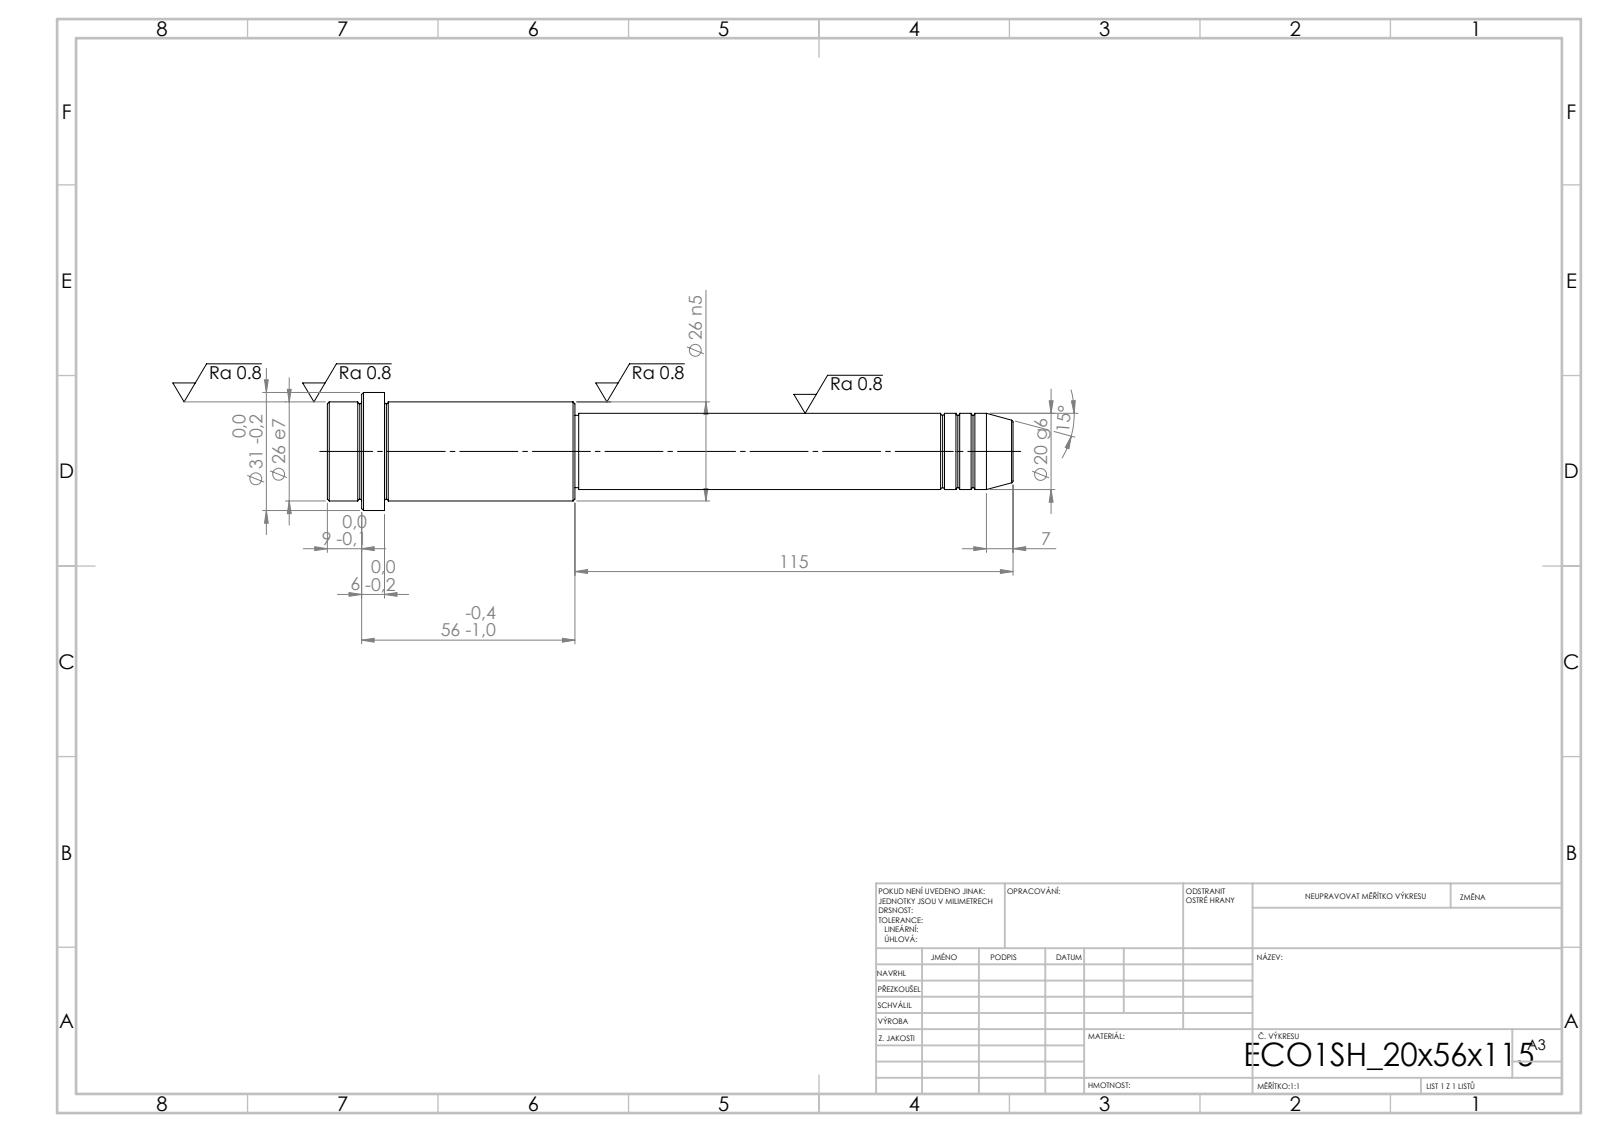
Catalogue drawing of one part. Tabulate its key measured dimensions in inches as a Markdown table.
| quantity | value |
| --- | --- |
| STEP written by | SolidWorks 2019 (CONFIG_CONTROL_DESIGN) |
| units | inches |
| bodies | 1 solid, 52 faces (6 planar, 16 cylindrical, 30 other) |
| overall size | 7.087 × 1.22 × 1.22 |
| volume | 4.357 in³ |
| surface area | 21.96 in² |
| round bosses / shafts (diameter × count) | 1.22 × 1, 1.024 × 1, 0.787 × 1, 0.748 × 1 |
| main face-to-face distances | 0.591, 1.969, 2.559, 4.528, 6.496, 7.087, 6.732, 2.205, 0.236, 0.354 |
